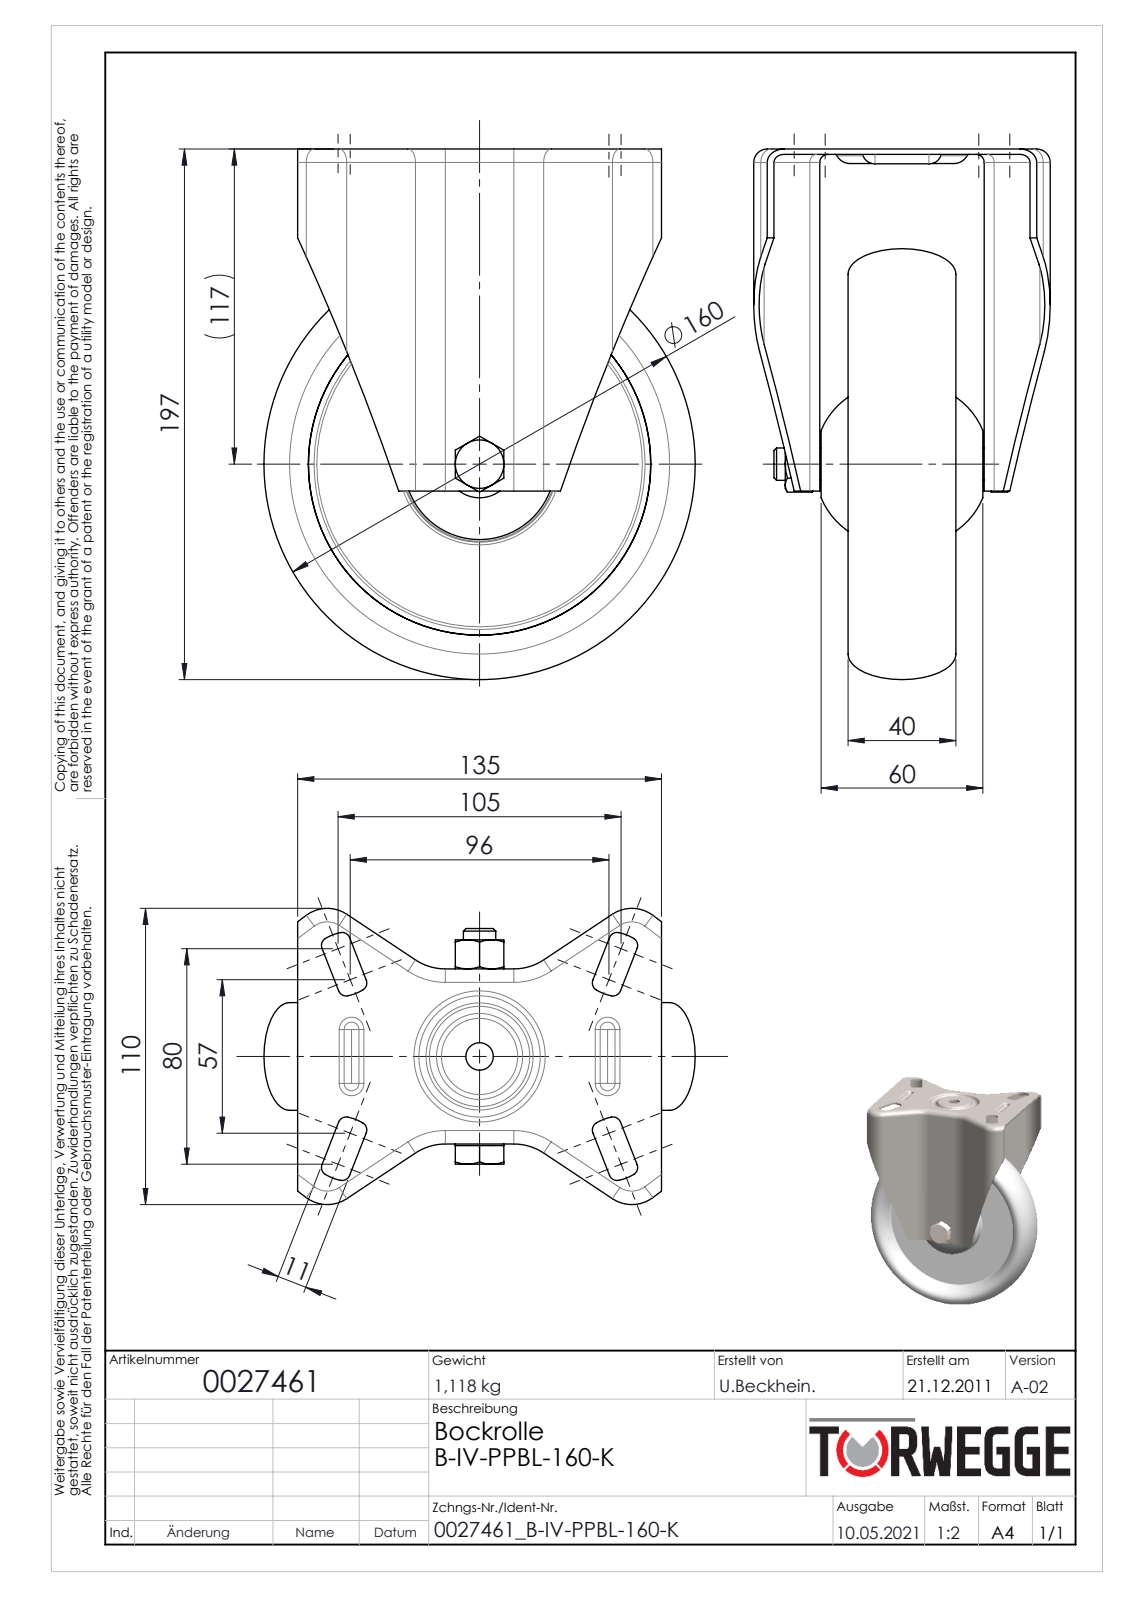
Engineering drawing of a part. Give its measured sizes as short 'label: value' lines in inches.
name: 0027461
written by: SolidWorks 2020 (AUTOMOTIVE_DESIGN)
unit: in
bodies: 7 solids, 341 faces (79 planar, 116 cylindrical, 146 other)
size: 7.756 × 6.284 × 4.331
volume: 32.58 in³; area: 332.2 in²
holes: 2× ⌀0.402, 1× ⌀0.472, 1× ⌀0.492, 1× ⌀1.772, 1× ⌀1.85
bosses: 1× ⌀1.614, 1× ⌀0.787, 1× ⌀0.709
rounds: 28× R0.118, 10× R0.197, 8× R0.703, 4× R0.079, 4× R0.181, 4× R0.433, 4× R0.512, 4× R0.787
face distances: 0.079, 1.235, 0.374, 1.314, 1.093, 1.467, 1.388, 1.157, 2.48, 1.014
